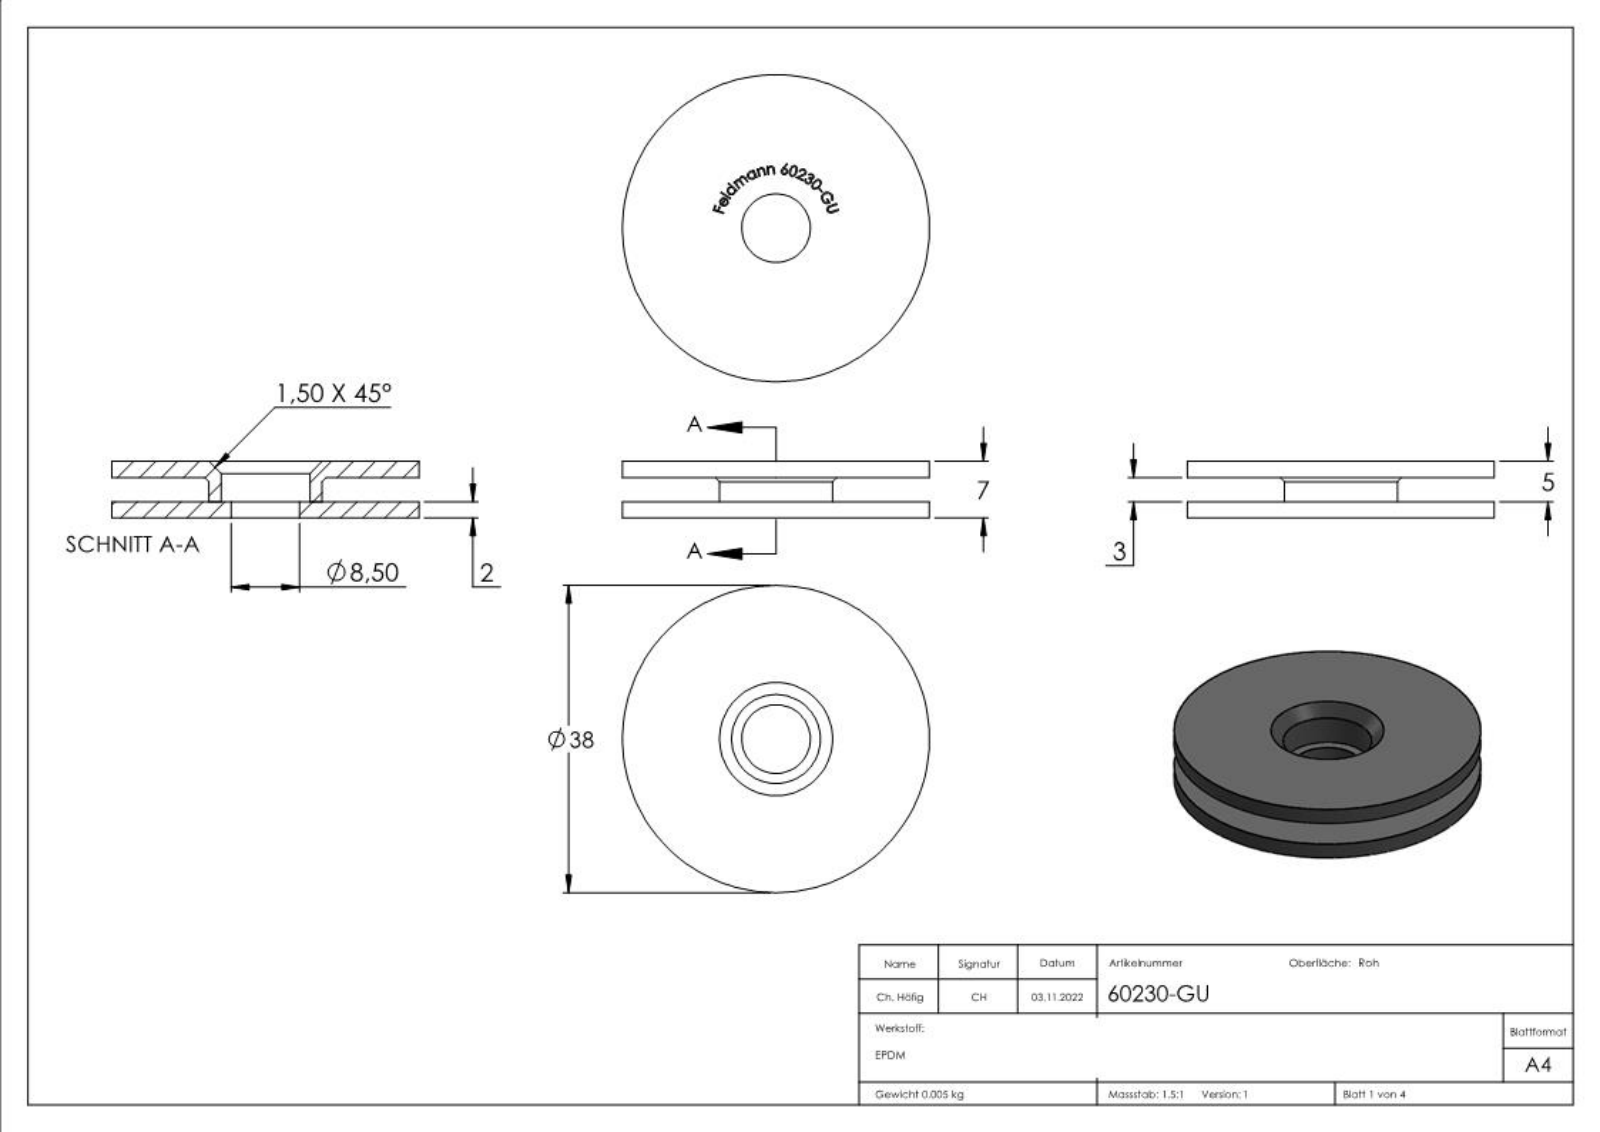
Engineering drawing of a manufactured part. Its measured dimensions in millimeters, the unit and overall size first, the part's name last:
Units: millimetres
Overall size (bounding box): 38 × 38 × 7
Round holes (diameter × count): ⌀8.5 ×1, ⌀11 ×1
Round bosses / shafts (diameter × count): ⌀38 ×1, ⌀14 ×1
Main face-to-face distances: 2, 5, 7, 3
Volume: 4 405 mm³ · Surface area: 5 014 mm²
Bodies: 2 solids, 20 faces (5 planar, 5 cylindrical, 10 other)
Part name (STEP PRODUCT): 60230-GU Teil2_60230-GU Teil2 Keyshot; 60230-GU Teil1_60230-GU Teil1 Keyshot; 60230-GU
STEP written by: SolidWorks 2018 (CONFIG_CONTROL_DESIGN)
